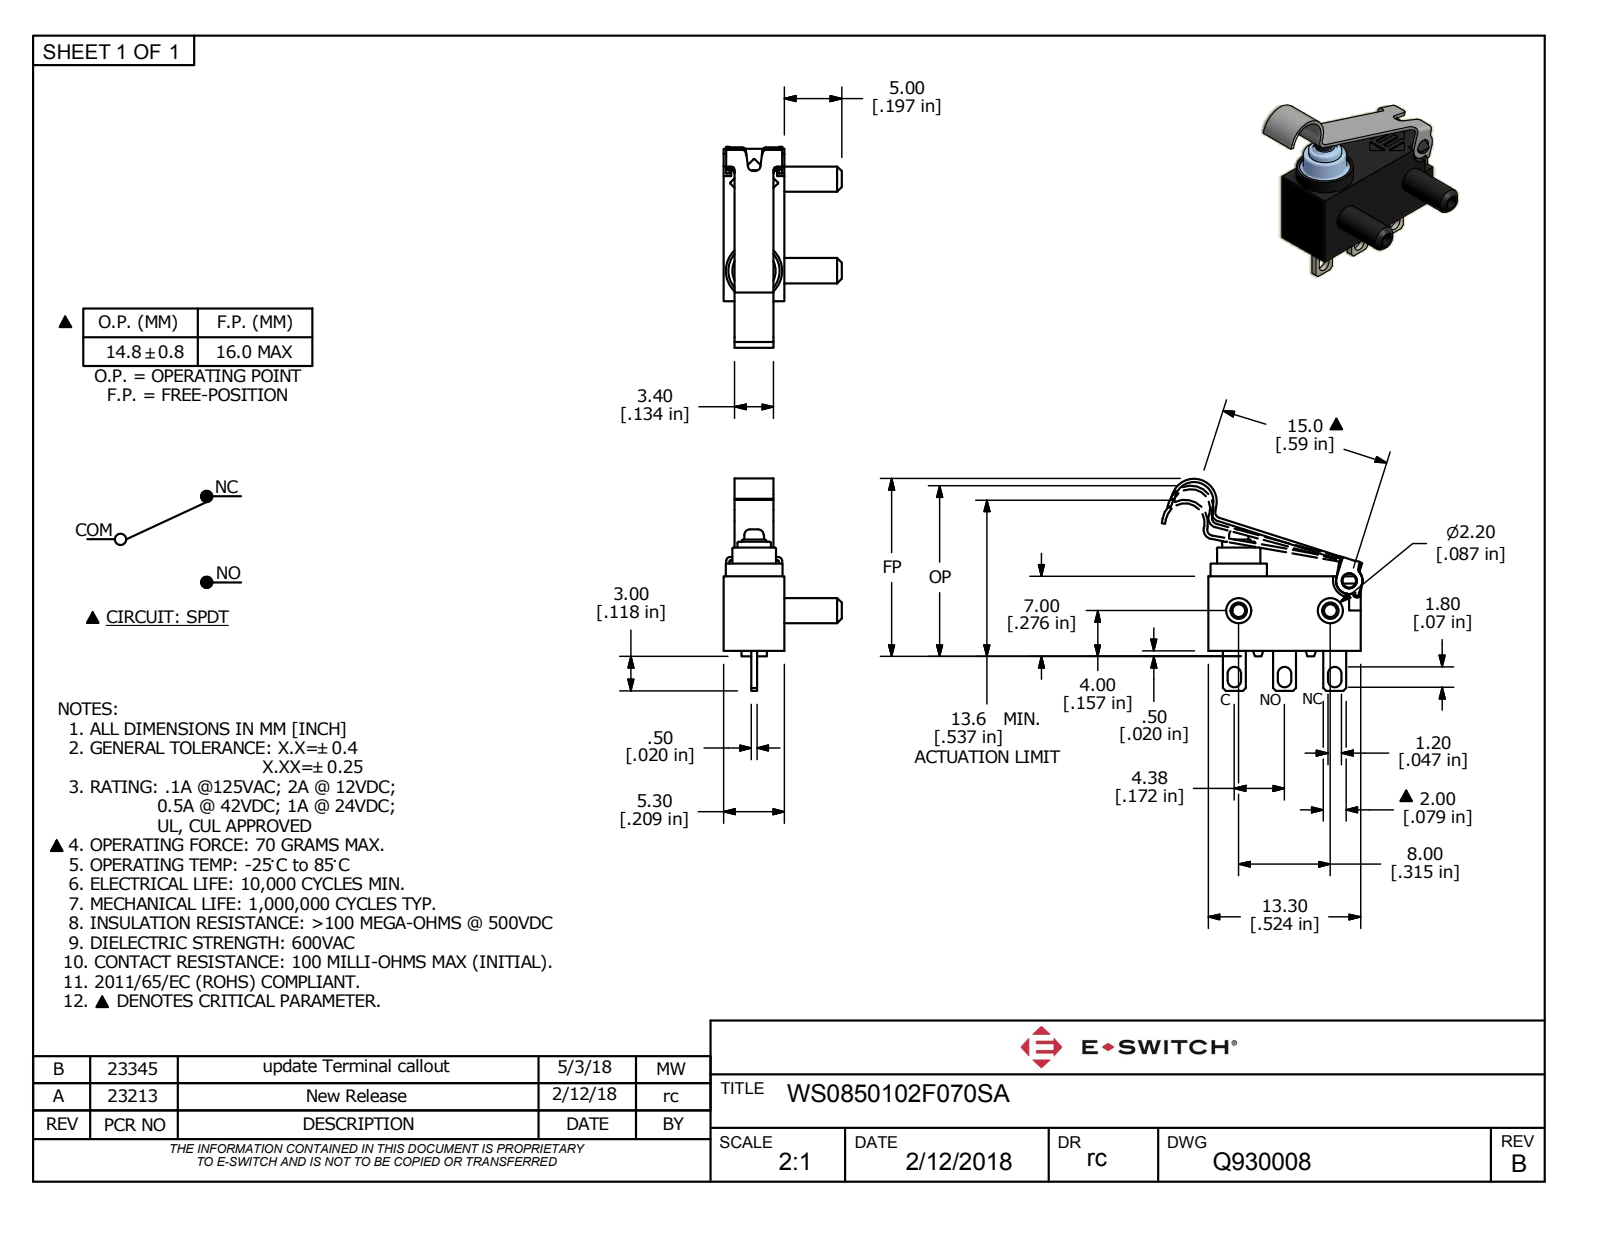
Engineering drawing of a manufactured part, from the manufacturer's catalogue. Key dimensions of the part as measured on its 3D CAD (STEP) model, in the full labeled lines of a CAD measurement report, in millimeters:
Part name (STEP PRODUCT): WS0850102F070SA
STEP written by: Autodesk Inventor 2012 (CONFIG_CONTROL_DESIGN)
Units: millimetres
Bodies: 2 solids, 197 faces (125 planar, 63 cylindrical, 9 other)
Overall size (bounding box): 18.5 × 16.7 × 10.3
Volume: 560 mm³ · Surface area: 770 mm²
Round holes (diameter × count): ⌀1.1 ×2, ⌀1.3 ×1, ⌀4.5 ×1
Round bosses / shafts (diameter × count): ⌀2.2 ×2, ⌀5 ×1, ⌀3.8 ×1, ⌀2.9 ×1, ⌀1.7 ×1
Partial cylindrical surfaces — rounded edges, fillets, slot ends (radius × count): R0.6 ×7, R0.3 ×6, R0.1 ×2, R0.3 ×2, R0.5 ×2, R0.5 ×1, R0.8 ×1, R1.1 ×1
Main face-to-face distances: 5.3, 6.5, 2.4, 2.9, 13.3, 0.5, 0.5, 4.1, 6.4, 4.3
Hole centre spacings: 3.1, 8, 10
